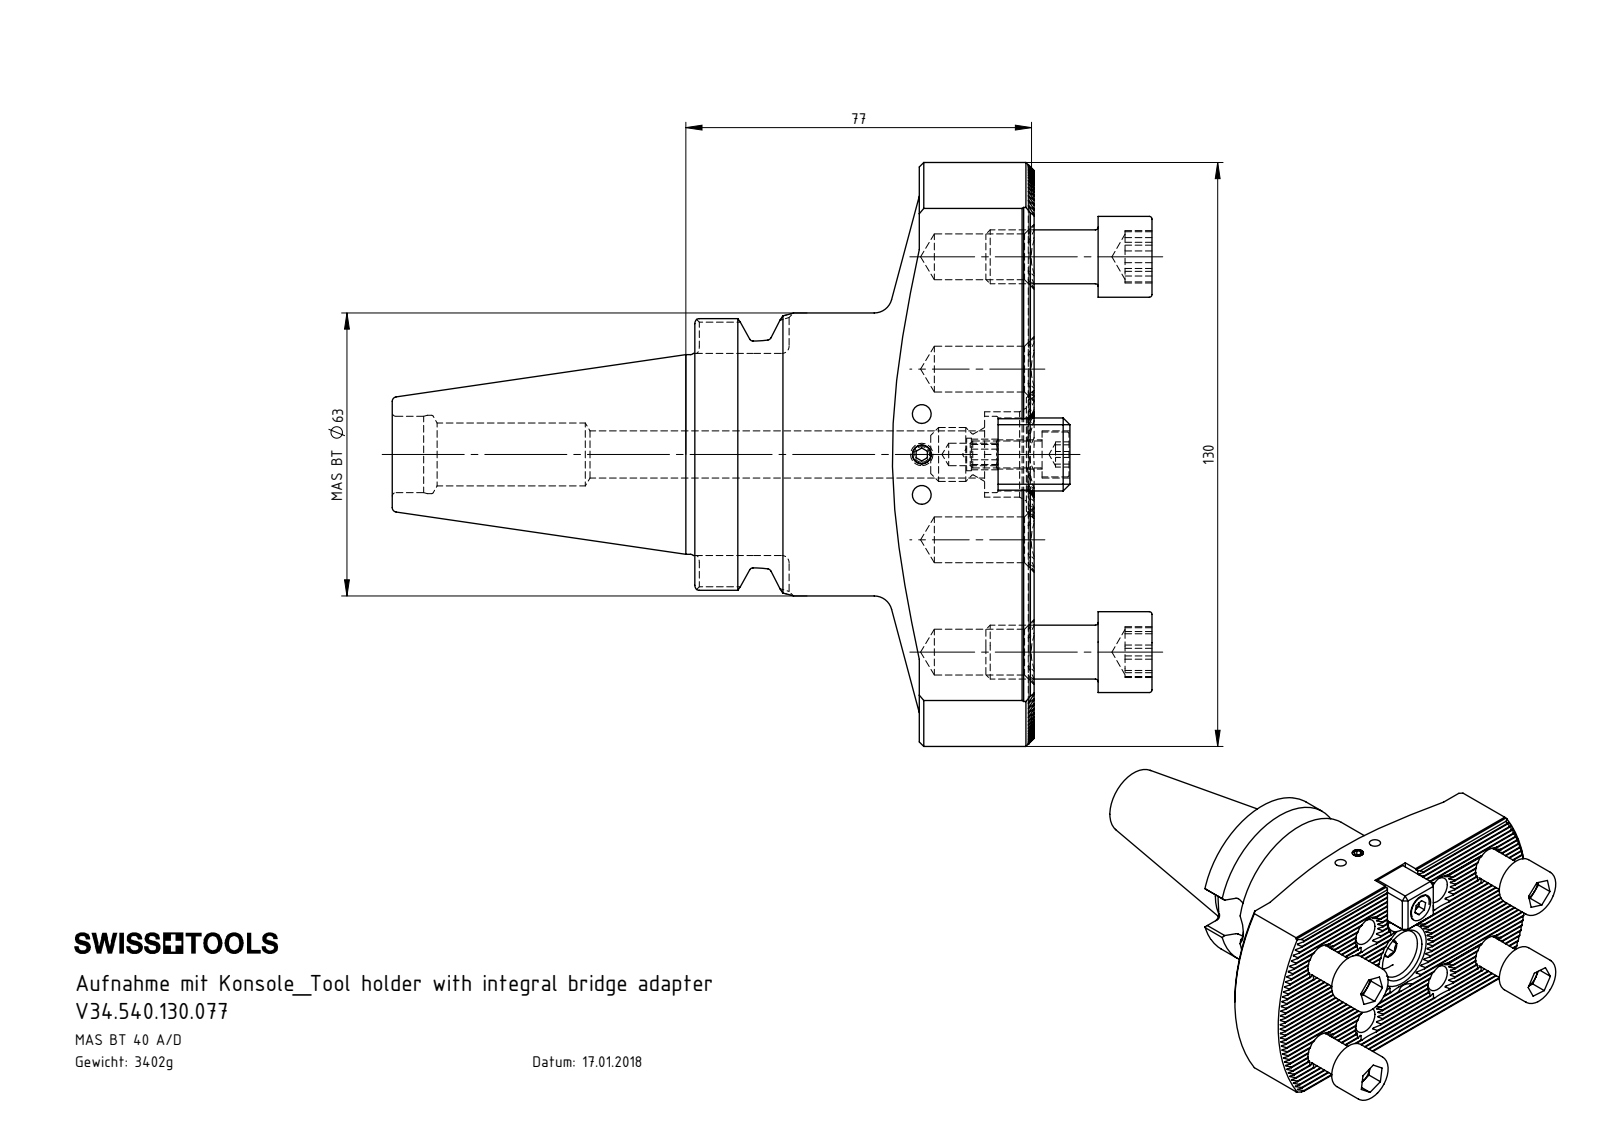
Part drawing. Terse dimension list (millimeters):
name: BT4-Ko1.K01.077_A; Ko1-ER1.001.016_A; ISO 4762 - M6 x 16; BT4.Ko1.K01.077 (+3 more)
written by: SolidWorks 2017 (AUTOMOTIVE_DESIGN)
unit: mm
bodies: 10 solids, 739 faces (487 planar, 161 cylindrical, 91 other)
size: 169.23 × 130 × 70
volume: 433 328 mm³; area: 73 073 mm²
holes: 8× ⌀10.2, 3× ⌀4.2, 2× ⌀10.5, 1× ⌀5, 1× ⌀6.5, 1× ⌀7.24, 1× ⌀14, 1× ⌀17, 1× ⌀17.45, 1× ⌀19
bosses: 5× ⌀12, 4× ⌀18, 1× ⌀63, 1× ⌀53, 1× ⌀44.45, 1× ⌀10, 1× ⌀6, 1× ⌀5
rounds: 34× R0.14, 8× R1.6, 1× R7.95, 1× R8.05, 1× R65
face distances: 1.73, 17.32, 70, 8.66, 3.46, 5.2, 6.93, 15.59, 19.05, 3.47
hole spacings: 25, 27.59, 40, 47.17, 48.33, 63, 74.63, 9
